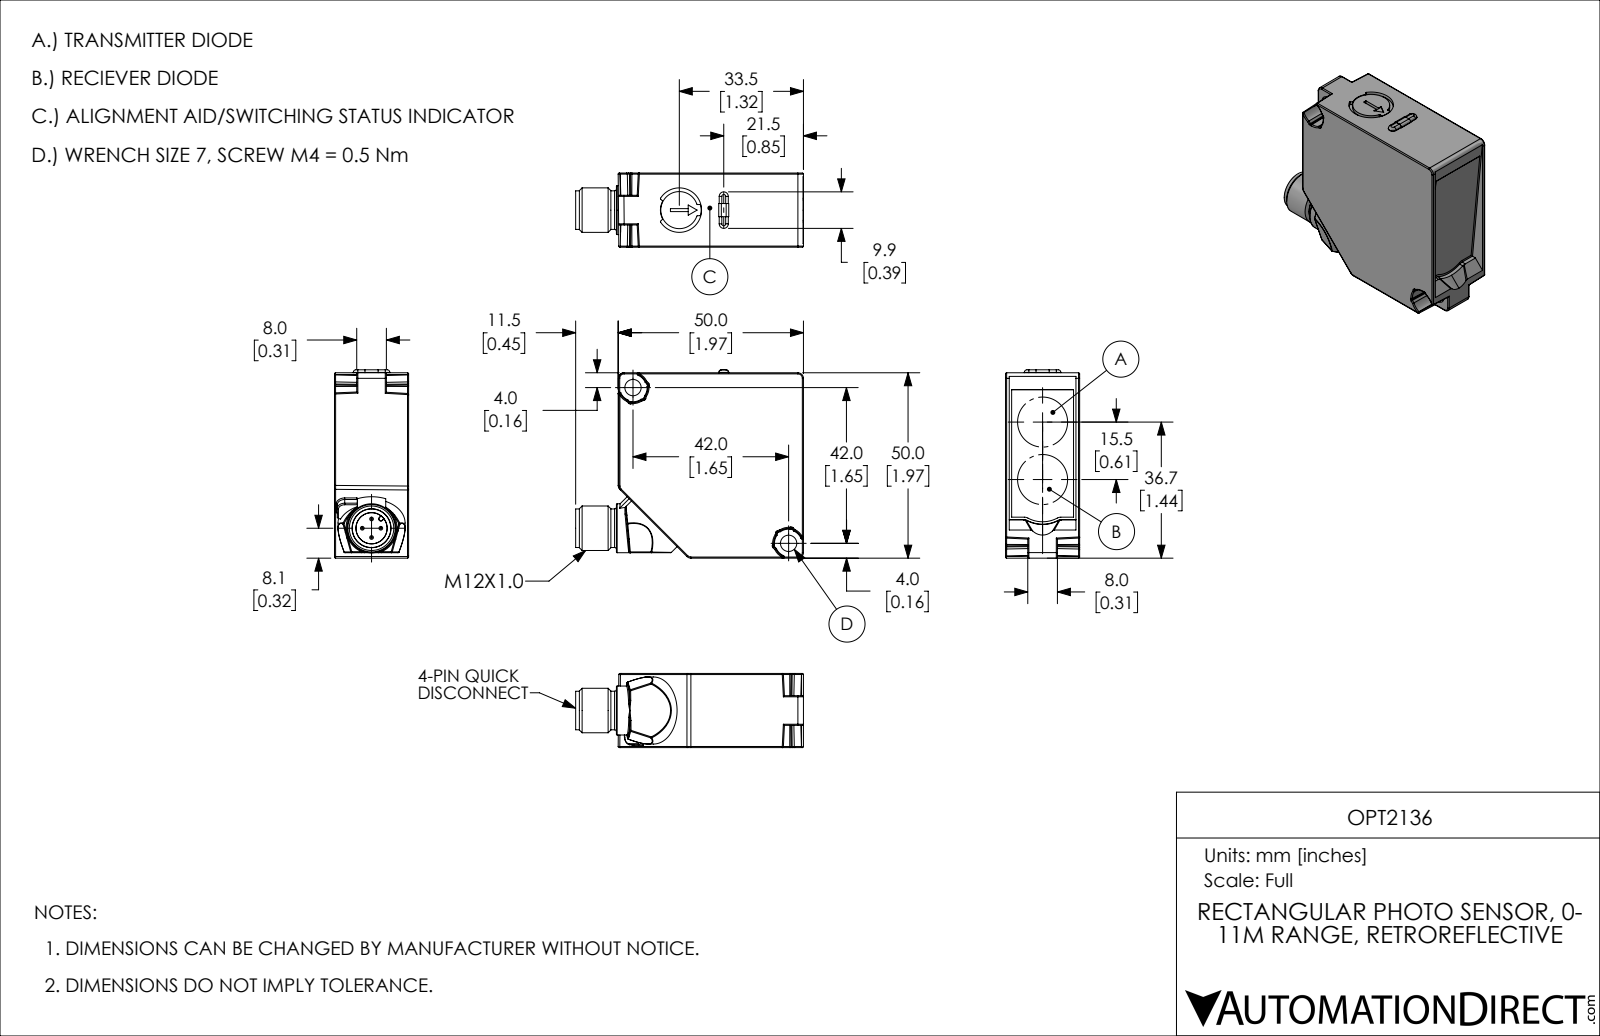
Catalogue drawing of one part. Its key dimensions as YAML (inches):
part_name: "OPT2136"
step_written_by: "SolidWorks 2019 (AUTOMOTIVE_DESIGN)"
units: inches
bodies: {solids: 2, faces: 342, planar: 110, cylindrical: 119, other: 113}
overall_size: [2.42, 2, 0.787]
volume: 2.816
surface_area: 16.5
round_holes:
  - {diameter: 0.173, count: 2}
  - {diameter: 0.472, count: 1}
  - {diameter: 0.713, count: 1}
round_bosses_or_shafts:
  - {diameter: 0.039, count: 4}
  - {diameter: 0.52, count: 1}
  - {diameter: 0.472, count: 1}
  - {diameter: 0.409, count: 1}
  - {diameter: 0.394, count: 1}
partial_cylinders:
  - {radius: 0.012, count: 63}
  - {radius: 0.008, count: 8}
  - {radius: 0.059, count: 5}
  - {radius: 0.079, count: 5}
  - {radius: 0.028, count: 4}
  - {radius: 0.048, count: 2}
  - {radius: 0.201, count: 1}
  - {radius: 0.232, count: 1}
face_to_face_distances: [0.787, 1.969, 0.039, 0.748, 0.236, 0.551, 0.197, 0.512, 0.058, 1.911]
hole_center_spacings: [2.339]
